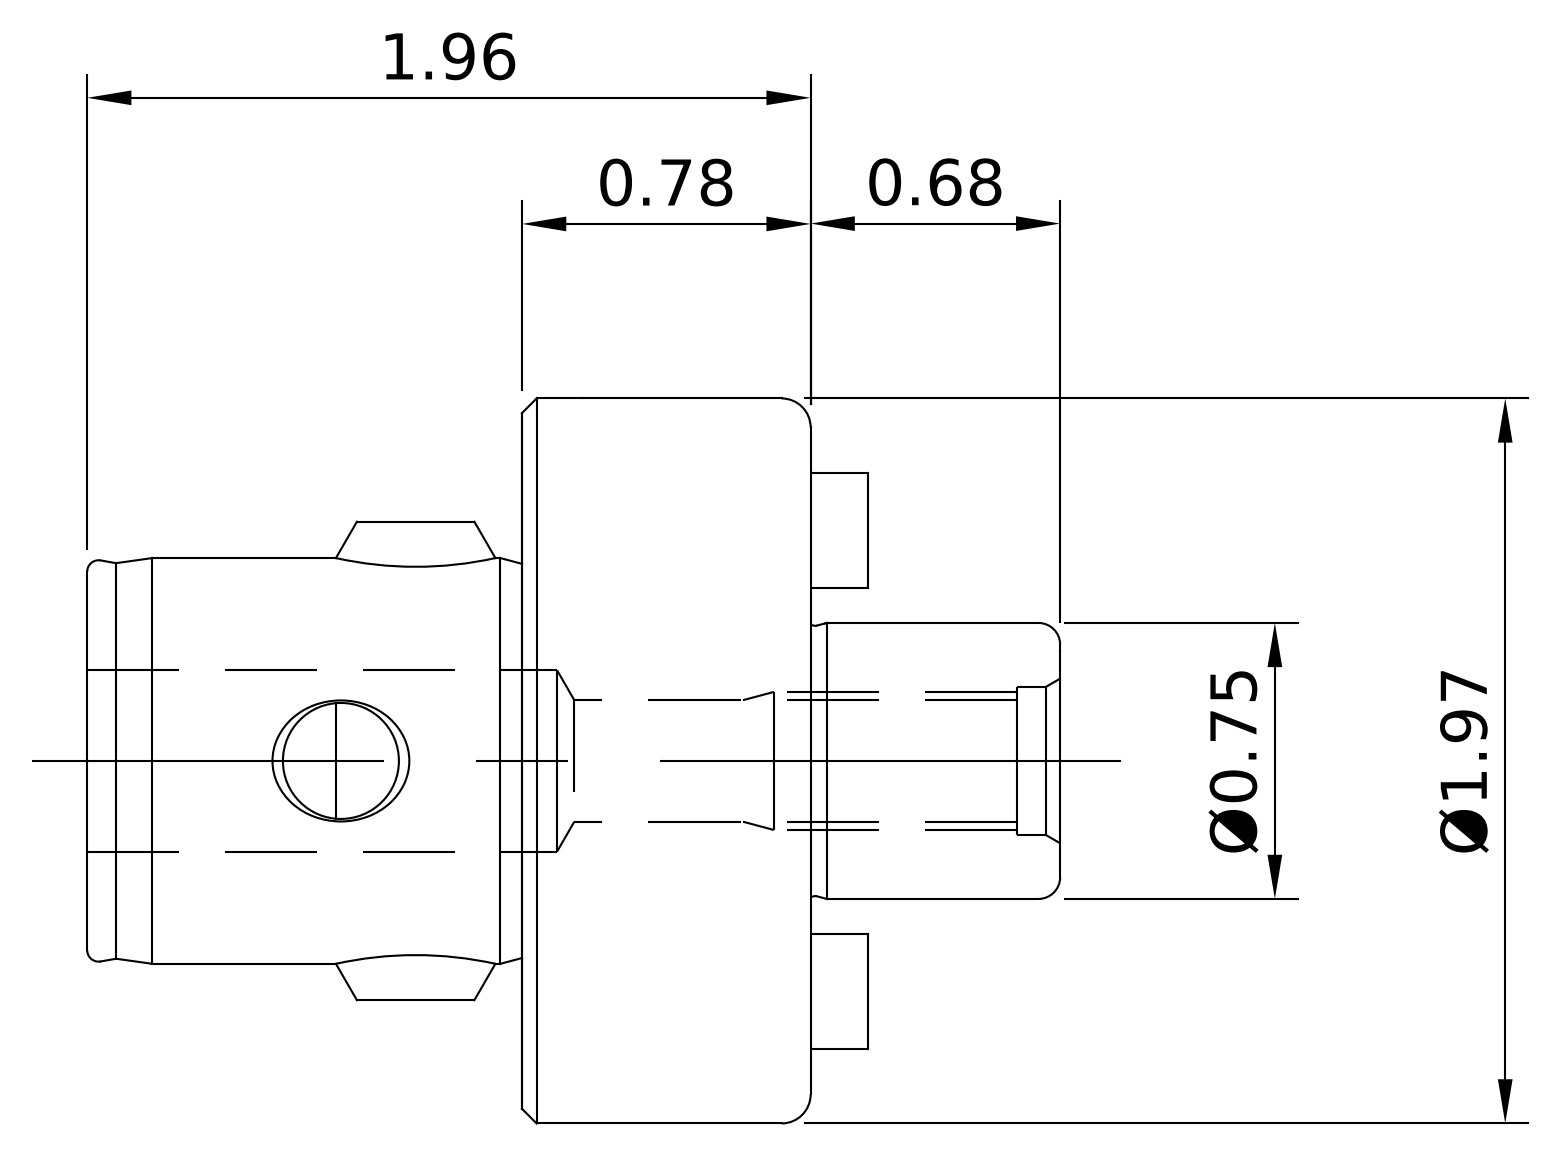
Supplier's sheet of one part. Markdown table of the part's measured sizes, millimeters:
| quantity | value |
| --- | --- |
| part name | 11.335.455_SMC MOD; 11.691.621; 10.691.50X_10.691.505; 691-50XRing_10.691.505Ring (+2 more) |
| STEP written by | SolidWorks 2016 (AUTOMOTIVE_DESIGN) |
| units | millimeters |
| bodies | 6 solids, 292 faces (62 planar, 99 cylindrical, 131 other) |
| overall size | 78.47 × 50 × 50 |
| volume | 60 808 mm³ |
| surface area | 18 991 mm² |
| round holes (diameter × count) | 2.5 × 3, 3 × 3, 3.25 × 3, 7.93 × 2, 6.48 × 1, 8 × 1, 8.43 × 1, 10.2 × 1, 11 × 1, 12.5 × 1, 14.5 × 1 |
| round bosses / shafts (diameter × count) | 7.95 × 2, 7.93 × 2, 50 × 1, 28 × 1, 22.1 × 1, 19.05 × 1, 10.9 × 1, 9.53 × 1 |
| partial cylindrical surfaces (radius × count) | 14 × 1 |
| main face-to-face distances | 19.9, 28.58, 30, 49.9, 9.53, 78.48, 48.48, 68.95, 38.95, 19.05 |
| hole center spacings | 7, 12.12, 10.43, 15.88, 17.35, 22.22, 25.9, 31.76 |
